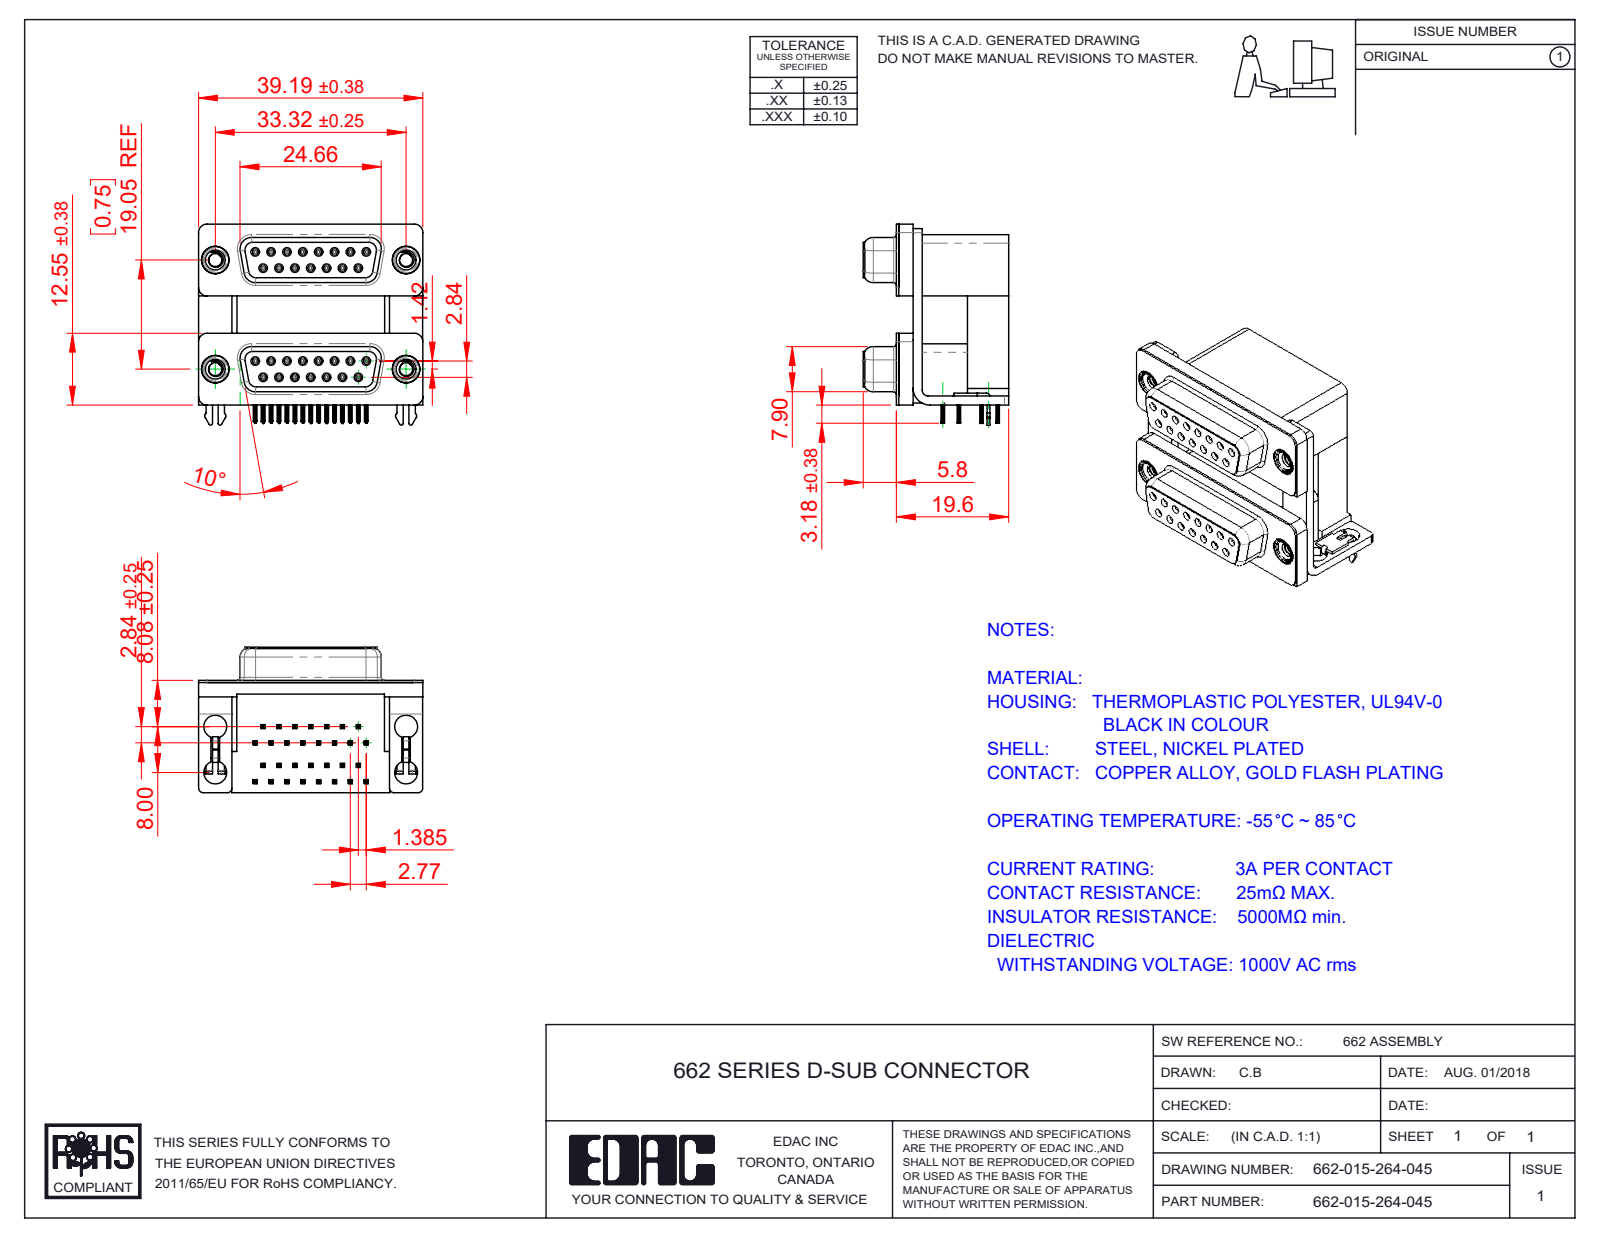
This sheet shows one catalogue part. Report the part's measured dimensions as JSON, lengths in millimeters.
{"part_name": "662 Shell_15 Contacts; 662 Contact Top Upper_M; 662 Housing Lower_15 Contacts; 662-015-264-045 (+8 more)", "step_written_by": "SolidWorks 2020 (CONFIG_CONTROL_DESIGN)", "units": "millimeters", "bodies": {"solids": 43, "faces": 4970, "planar": 2274, "cylindrical": 1204, "other": 1492}, "overall_size": [39.19, 35.1, 25.4], "volume_mm3": 16007, "surface_area_mm2": 18091, "round_holes": [[0.8, 30], [0.9, 30], [4, 8], [2.26, 4], [3.5, 4], [4.8, 4], [5, 4]], "round_bosses_or_shafts": [[1.2, 30], [4.9, 4], [4.75, 4], [3.9, 4]], "partial_cylinders_radius": [[0.1, 241], [0.15, 120], [0.35, 60], [0.34, 30], [1.35, 16], [1.5, 16], [0.28, 14], [0.5, 12]], "face_to_face_distances": [19.05, 0.4, 19.2, 12, 2.5, 16.7, 7.2, 9.5, 2.9, 10.7], "hole_center_spacings": [3.16, 19.25, 2.77, 19.84, 5.54, 8.31, 19.05, 20.78]}
